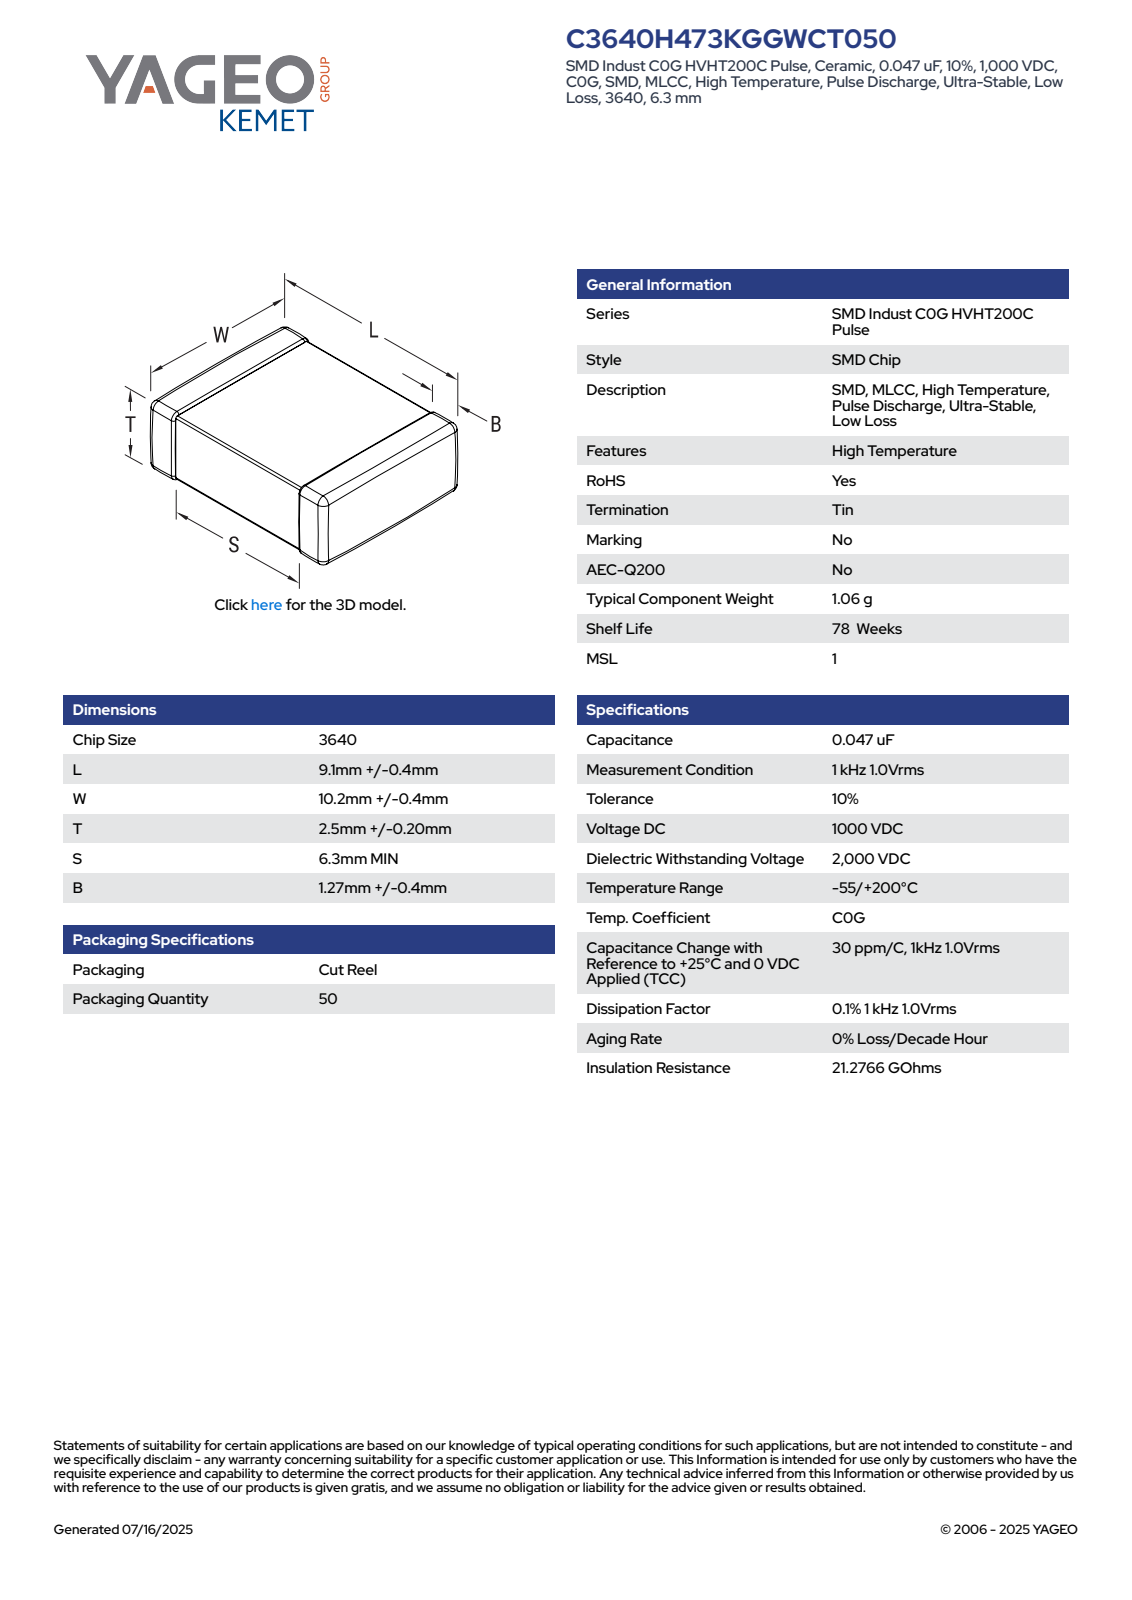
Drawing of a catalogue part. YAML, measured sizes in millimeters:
part_name: "CCS_CCSTDNOS_3640_L9.5W10.6T2.7B1.67"
step_written_by: "SolidWorks 2014 (AUTOMOTIVE_DESIGN)"
units: millimeters
bodies: {solids: 4, faces: 121, planar: 71, cylindrical: 34, other: 16}
overall_size: [10.6, 9.5, 2.7]
volume: 235
surface_area: 300
partial_cylinders:
  - {radius: 0.22, count: 24}
face_to_face_distances: [2.26, 2.48, 2.7, 9.5, 10.16, 10.38, 10.6, 0.67, 5.4, 5.18]
